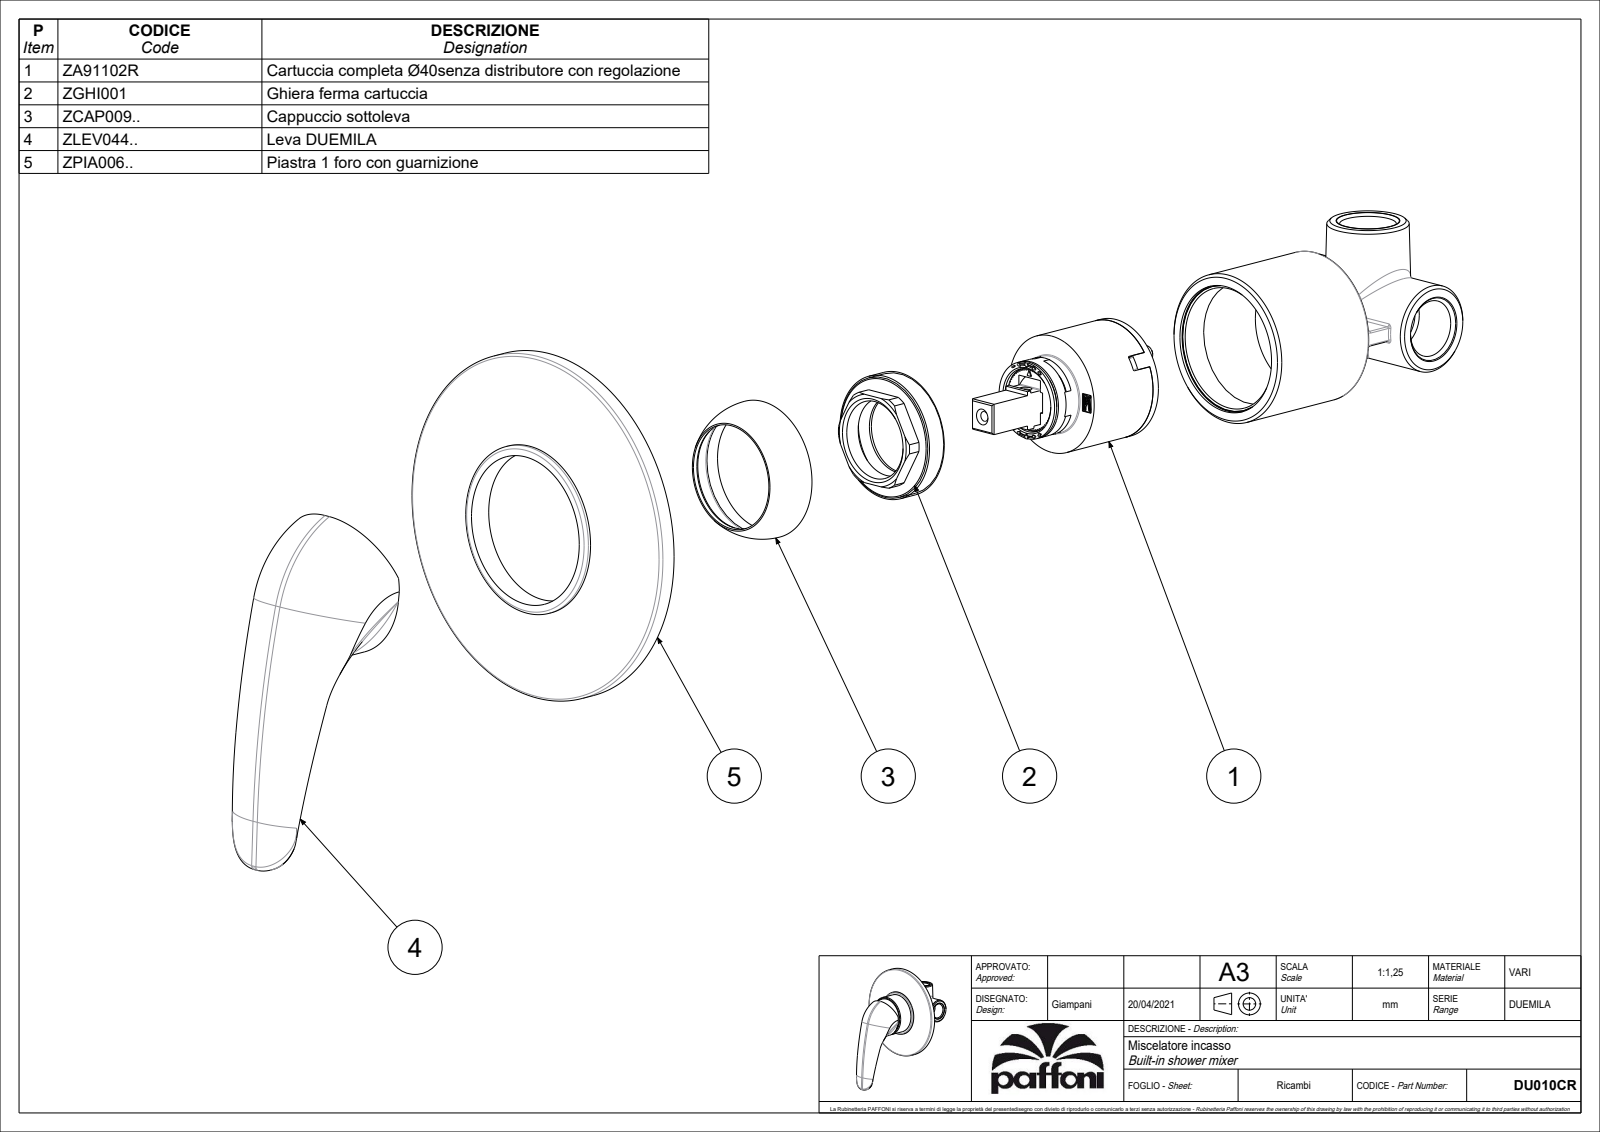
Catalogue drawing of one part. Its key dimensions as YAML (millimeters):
part_name: "DU010CR"
step_written_by: "CREO PARAMETRIC BY PTC INC, 2020044 (CONFIG_CONTROL_DESIGN)"
units: millimeters
bodies: {solids: 1, faces: 84, planar: 20, cylindrical: 24, other: 40}
overall_size: [149.67, 116, 77.02]
volume: 186247
surface_area: 42231
round_holes:
  - {diameter: 4.5, count: 1}
  - {diameter: 9.2, count: 1}
round_bosses_or_shafts:
  - {diameter: 116, count: 1}
  - {diameter: 56.5, count: 1}
  - {diameter: 50, count: 1}
  - {diameter: 18.1, count: 1}
partial_cylinders:
  - {radius: 1.5, count: 2}
  - {radius: 15, count: 2}
  - {radius: 24, count: 2}
  - {radius: 24.5, count: 2}
  - {radius: 18, count: 1}
  - {radius: 39.04, count: 1}
  - {radius: 340.59, count: 1}
  - {radius: 341.58, count: 1}
face_to_face_distances: [45.5, 11, 34.5, 31, 20, 14.5, 9, 2, 22, 36.5]
